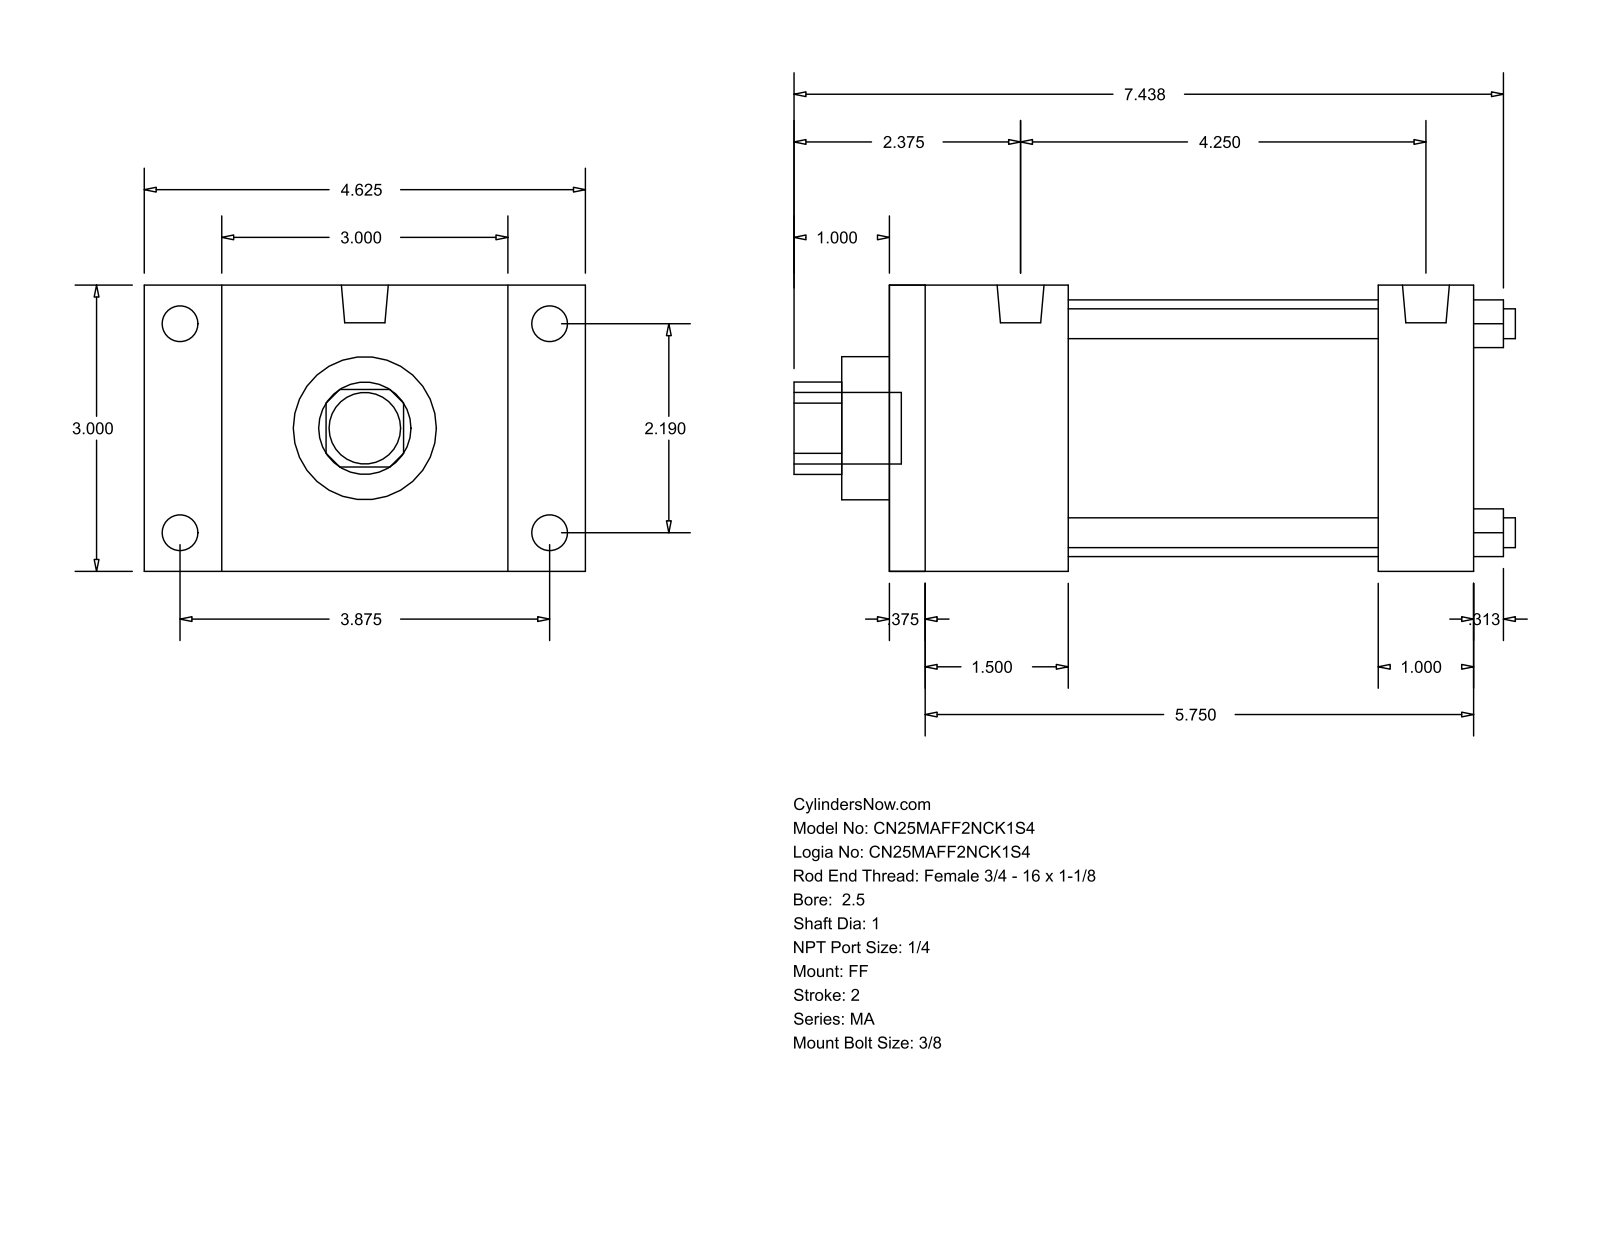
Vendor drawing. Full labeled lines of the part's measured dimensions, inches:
Part name (STEP PRODUCT): MA_FF__0250_1
STEP written by: GSSL Pune (CONFIG_CONTROL_DESIGN)
Units: inches
Bodies: 0 solids, 92 faces (64 planar, 28 cylindrical, 0 other)
Overall size (bounding box): 7.563 × 4.625 × 3
Round holes (diameter × count): ⌀0.313 ×4, ⌀1 ×1, ⌀1.5 ×1, ⌀2.69 ×1
Round bosses / shafts (diameter × count): ⌀0.375 ×4, ⌀0.313 ×4, ⌀0.492 ×2, ⌀0.75 ×1
Partial cylindrical surfaces — rounded edges, fillets, slot ends (radius × count): R0.484 ×1
Main face-to-face distances: 3, 6.125, 0.375, 5.75, 1, 1.875, 5.125, 1.5, 4.75, 3.25
Hole centre spacings: 1.548, 2.19, 3.097
